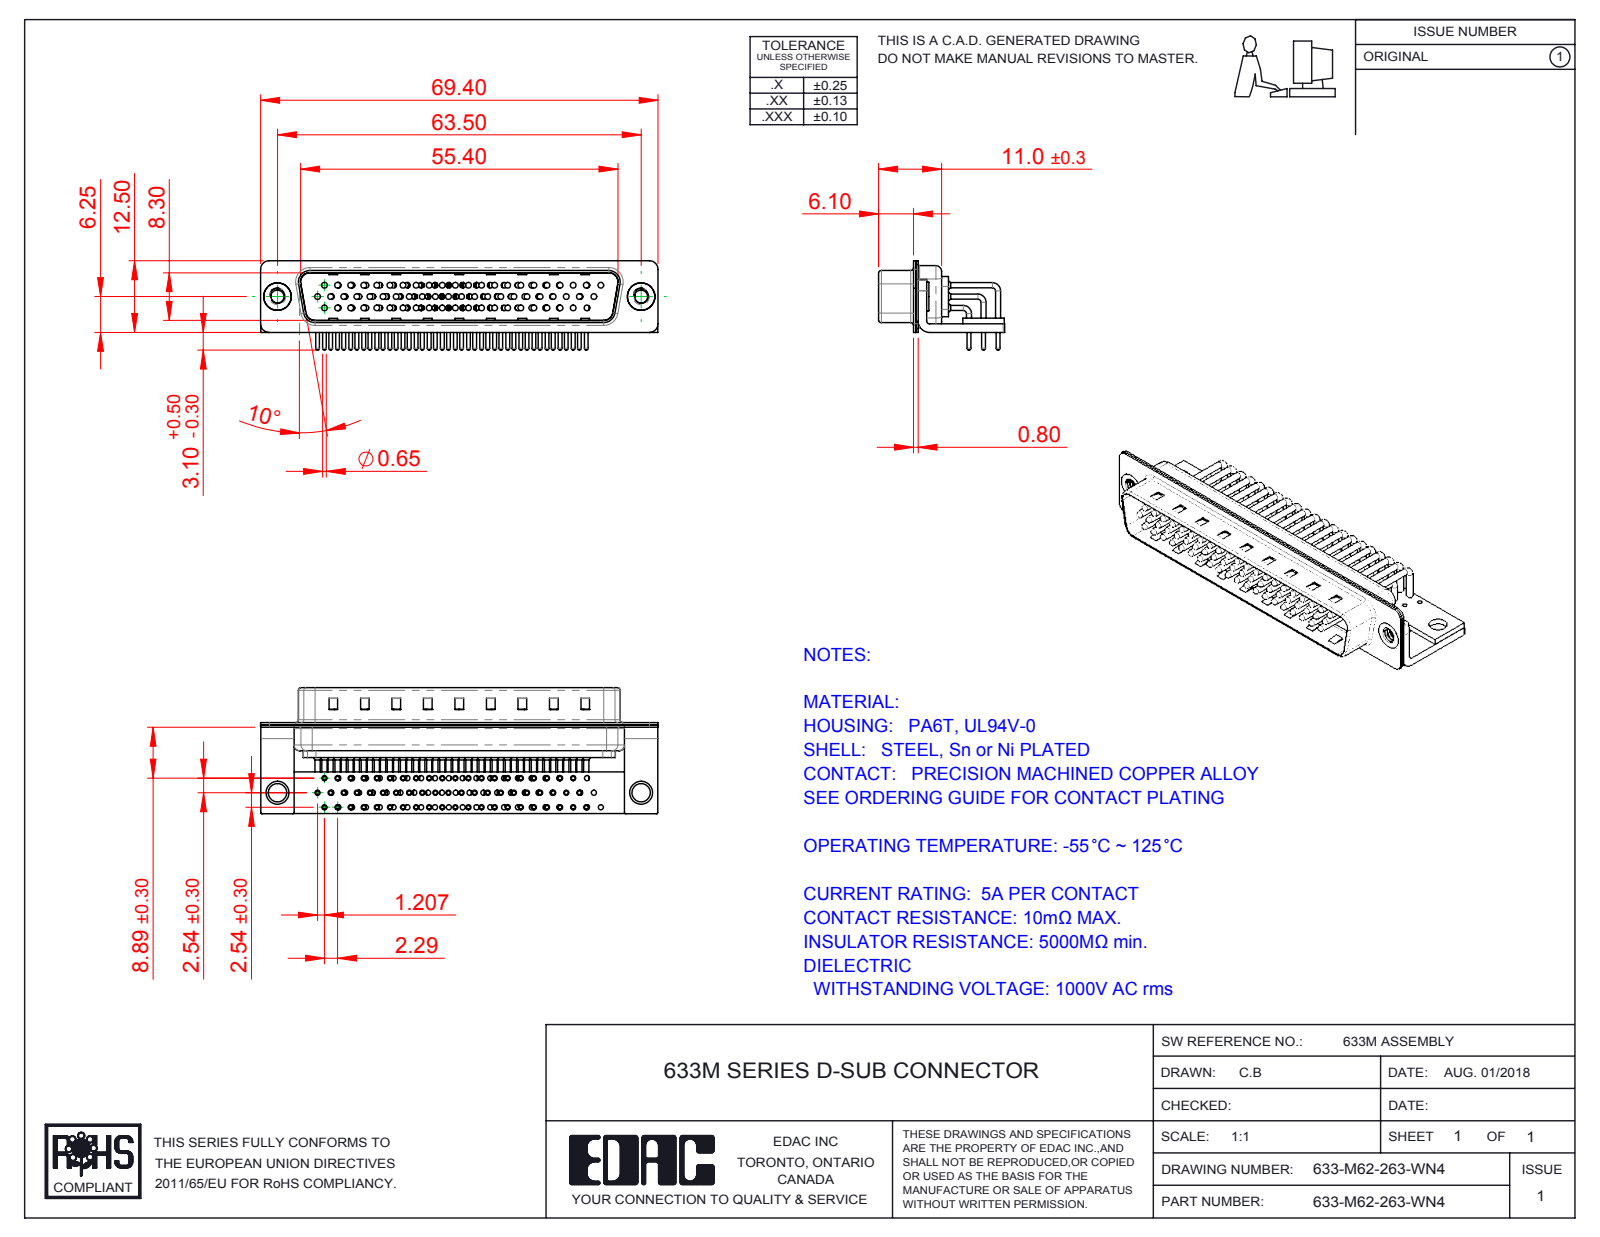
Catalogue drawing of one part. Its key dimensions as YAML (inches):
part_name: "633M Contact Row 1; 633M Shell Front_62 Contacts; 633M Shell Rear_62 Contacts; 633M Contact Row 3 (+6 more)"
step_written_by: "SolidWorks 2016 (CONFIG_CONTROL_DESIGN)"
units: inches
bodies: {solids: 70, faces: 7406, planar: 4197, cylindrical: 2519, other: 690}
overall_size: [2.732, 0.866, 0.614]
volume: 0.31
surface_area: 24.01
round_holes:
  - {diameter: 0.035, count: 62}
  - {diameter: 0.039, count: 62}
  - {diameter: 0.067, count: 62}
  - {diameter: 0.079, count: 62}
  - {diameter: 0.089, count: 2}
  - {diameter: 0.126, count: 2}
  - {diameter: 0.157, count: 2}
  - {diameter: 0.189, count: 2}
round_bosses_or_shafts:
  - {diameter: 0.035, count: 118}
  - {diameter: 0.059, count: 62}
  - {diameter: 0.026, count: 62}
  - {diameter: 0.039, count: 56}
  - {diameter: 0.197, count: 2}
  - {diameter: 0.193, count: 2}
partial_cylinders:
  - {radius: 0.04, count: 62}
  - {radius: 0.01, count: 16}
  - {radius: 0.059, count: 16}
  - {radius: 0.079, count: 13}
  - {radius: 0.02, count: 9}
  - {radius: 0.063, count: 8}
  - {radius: 0.024, count: 4}
  - {radius: 0.026, count: 4}
face_to_face_distances: [0.016, 0.033, 0.049, 0.059, 0.376, 0.039, 0.075, 0.409, 0.031, 0.327]
hole_center_spacings: [0.285, 0.095, 0.38, 0.19, 0.57, 0.665, 0.111, 0.091]
